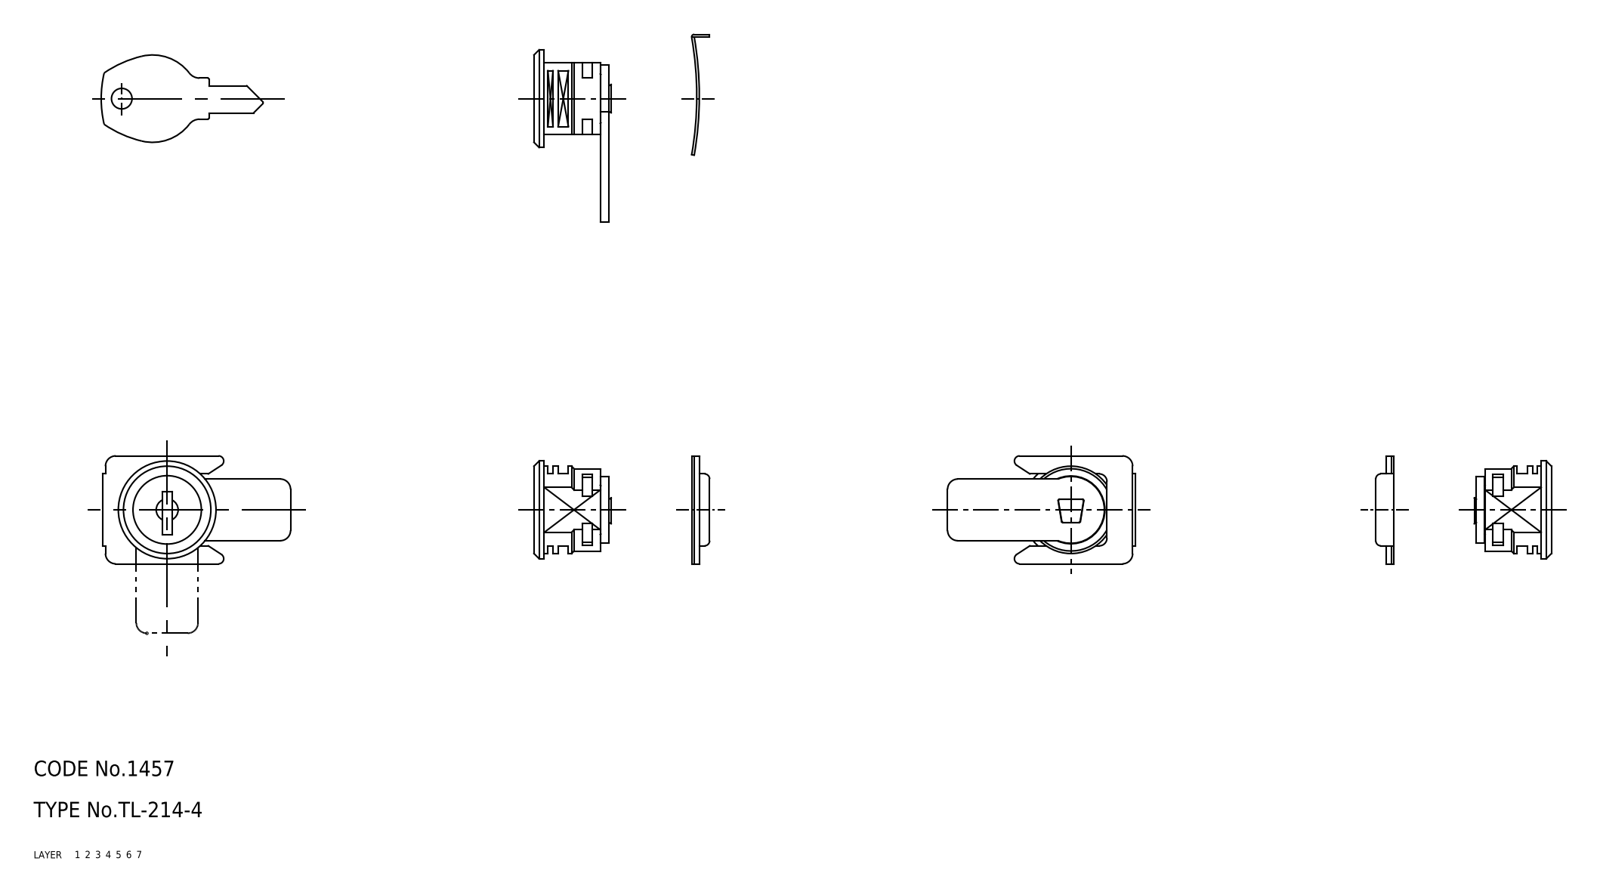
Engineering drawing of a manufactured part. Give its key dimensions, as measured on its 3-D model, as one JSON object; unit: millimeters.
{"part_name": "cam_mr; retainer_mr; lock; key (+1 more)", "step_written_by": "CADfix (AUTOMOTIVE_DESIGN)", "units": "millimeters", "bodies": {"solids": 5, "faces": 112, "planar": 0, "cylindrical": 0, "other": 112}, "overall_size": [67.75, 36.5, 21], "volume_mm3": 3852, "surface_area_mm2": 4598}
